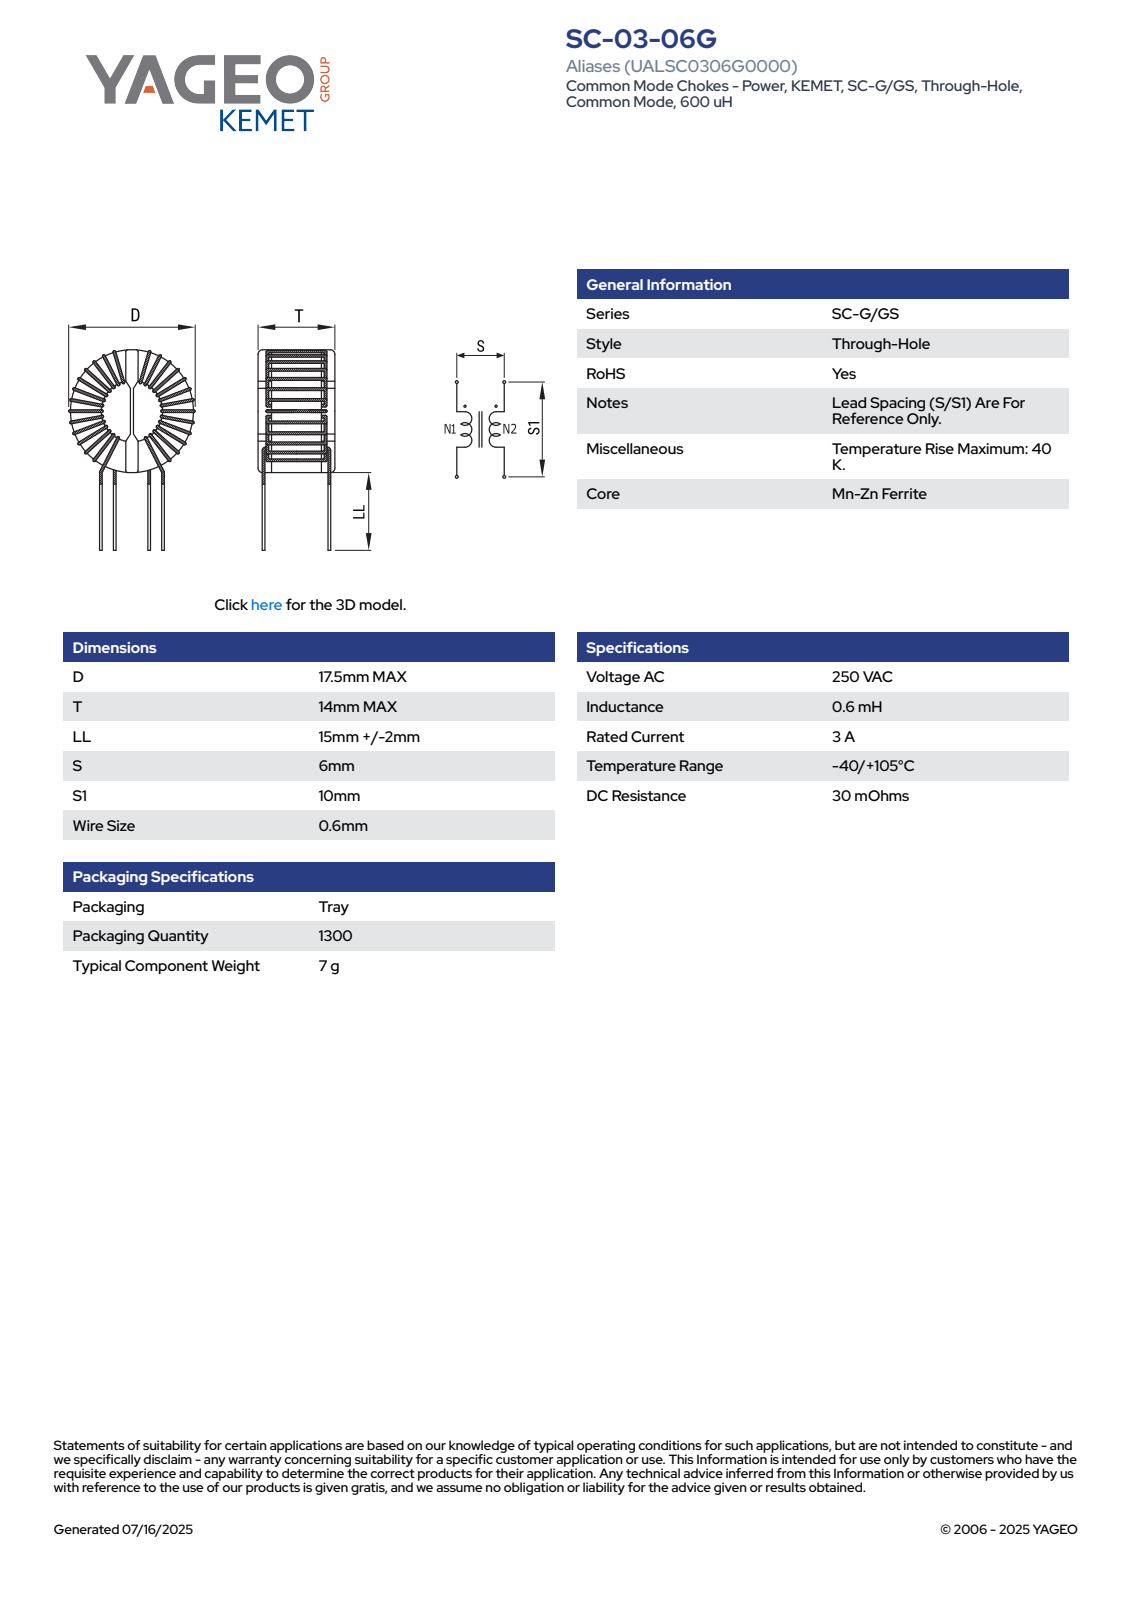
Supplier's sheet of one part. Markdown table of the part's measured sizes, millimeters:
| quantity | value |
| --- | --- |
| part name | SC-03-06G |
| STEP written by | SolidWorks 2018 (AUTOMOTIVE_DESIGN) |
| units | millimeters |
| bodies | 4 solids, 251 faces (108 planar, 67 cylindrical, 76 other) |
| overall size | 30.35 × 17.5 × 14 |
| volume | 2 393 mm³ |
| surface area | 3 289 mm² |
| round holes (diameter × count) | 7.6 × 1, 12.81 × 1 |
| round bosses / shafts (diameter × count) | 0.6 × 8, 13.63 × 1, 12.8 × 1, 12.7 × 1, 7.25 × 1 |
| partial cylindrical surfaces (radius × count) | 0.3 × 18, 2.32 × 1, 3.21 × 1, 3.67 × 1, 6.82 × 1, 8.75 × 1 |
| main face-to-face distances | 1.2, 2, 8.15, 1.75, 8.3, 6.55, 3.2, 1.6, 0.8, 0.56 |
